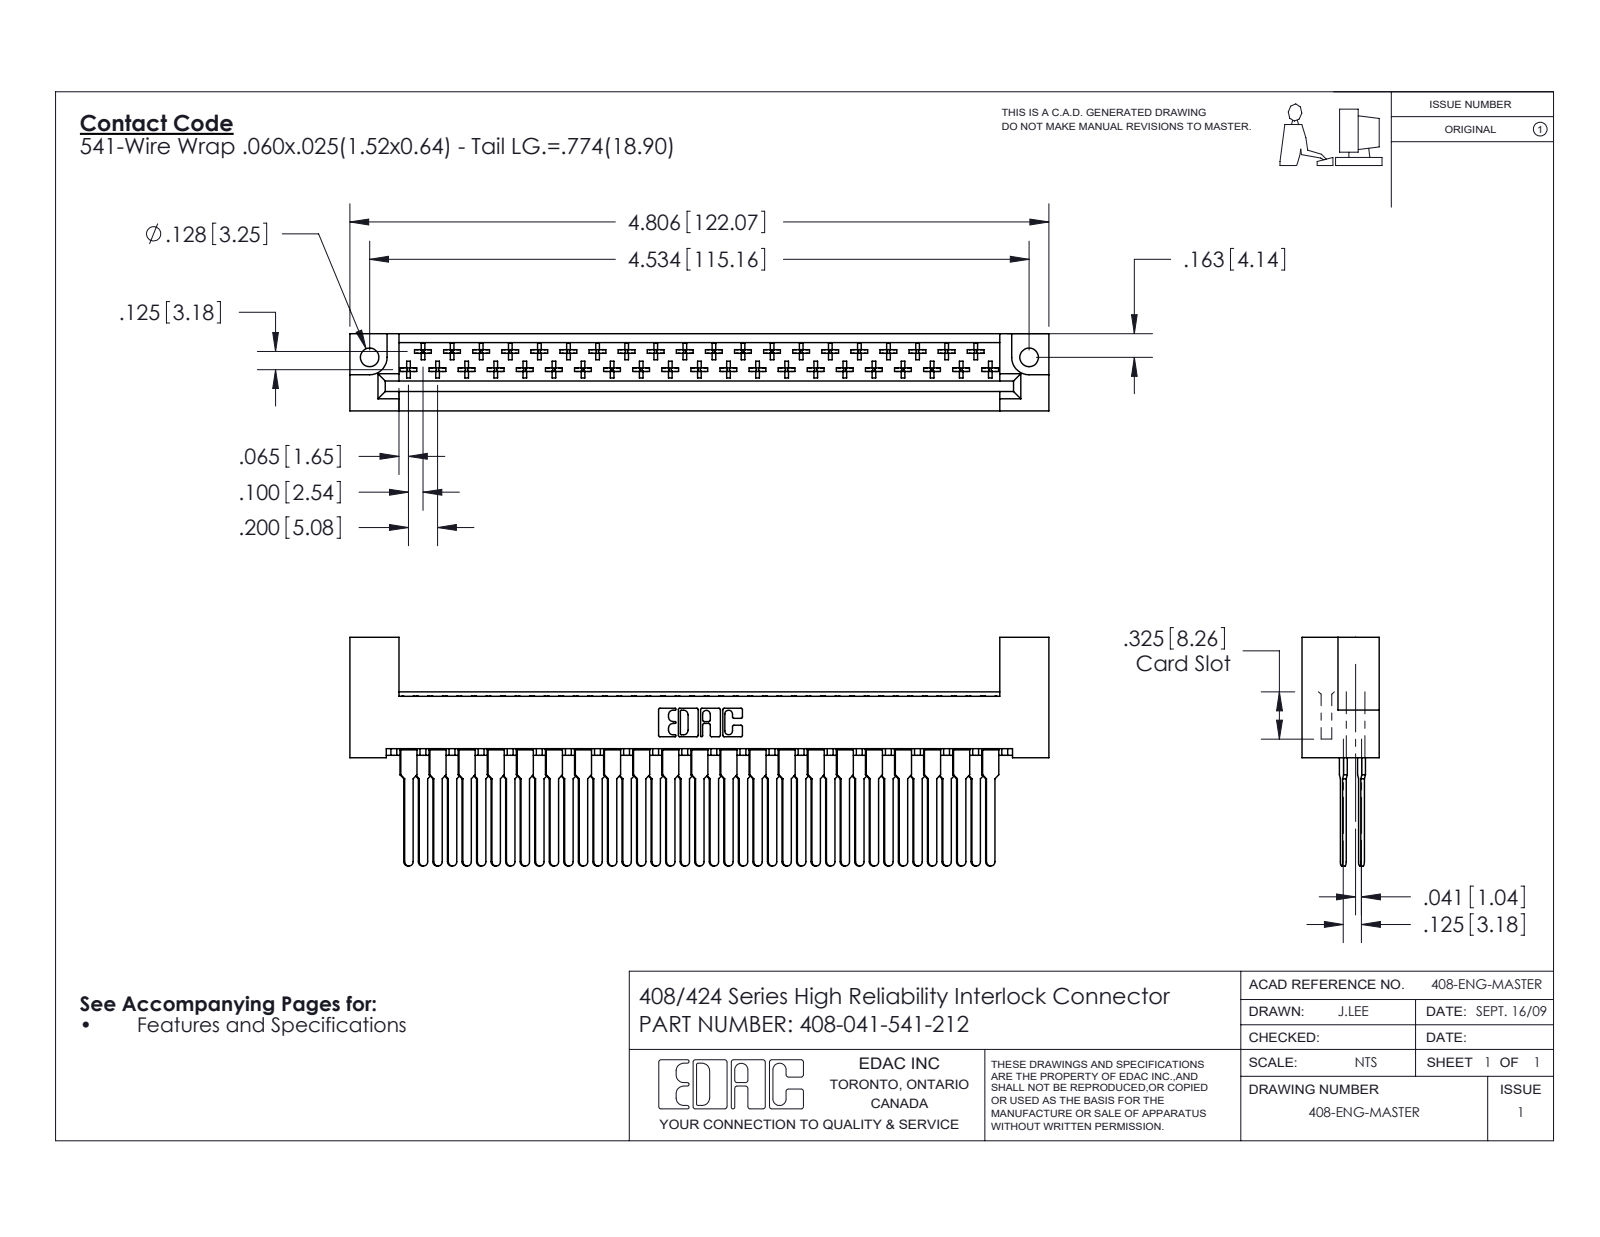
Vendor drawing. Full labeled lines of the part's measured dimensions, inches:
Part name (STEP PRODUCT): 408-047-541-212; 408 Part_041 - 2; 408-290-001_408-290-141
STEP written by: SolidWorks 2016 (CONFIG_CONTROL_DESIGN)
Units: inches
Bodies: 42 solids, 2312 faces (1729 planar, 419 cylindrical, 164 other)
Overall size (bounding box): 4.806 × 1.572 × 0.531
Volume: 0.963 in³ · Surface area: 32.06 in²
Round holes (diameter × count): ⌀0.128 ×2
Partial cylindrical surfaces — rounded edges, fillets, slot ends (radius × count): R0.01 ×246, R0.02 ×43, R0.03 ×41, R0.01 ×22, R0.007 ×6, R0.031 ×6, R0.026 ×3, R0.12 ×2
Main face-to-face distances: 0.531, 0.125, 0.1, 0.025, 0.025, 0.361, 0.235, 0.259, 0.217, 0.272
Hole centre spacings: 4.534
